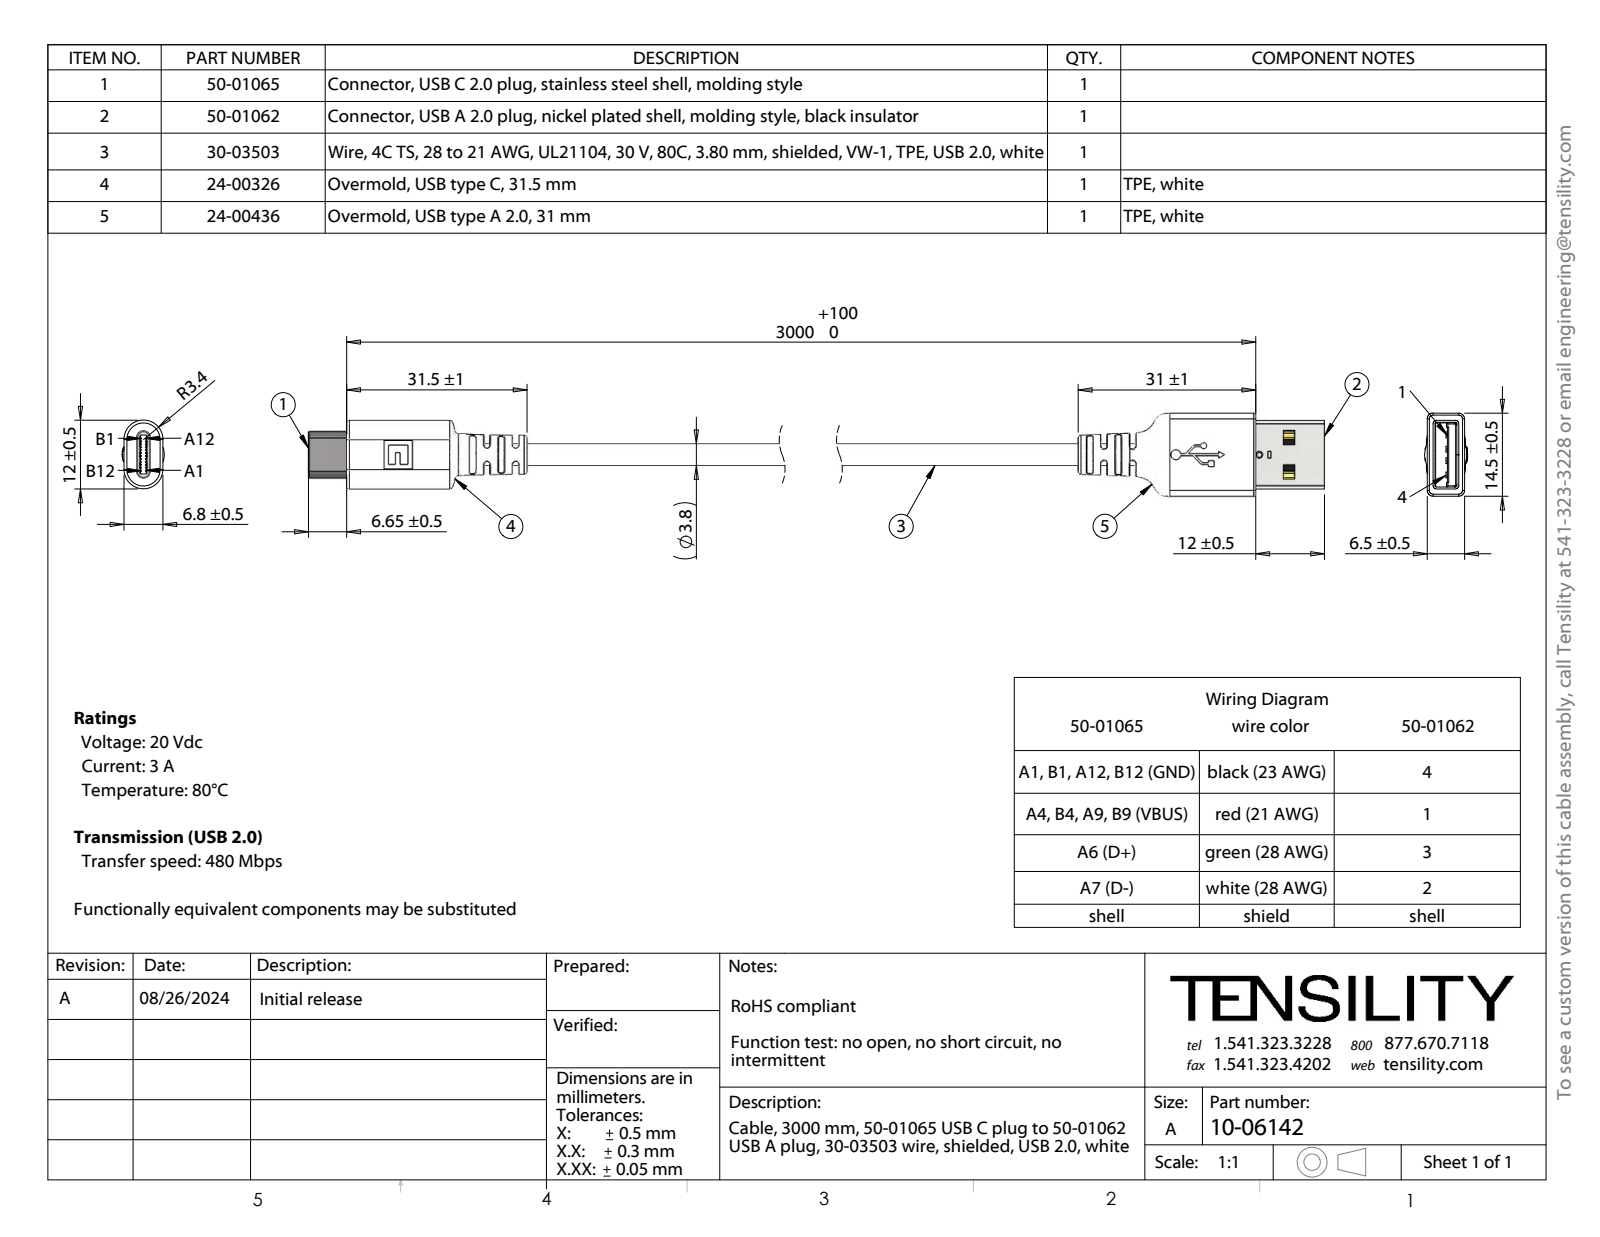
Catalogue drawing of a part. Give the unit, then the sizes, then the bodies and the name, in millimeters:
Units: millimetres
Overall size (bounding box): 211.15 × 14.5 × 7.54
Round holes (diameter × count): ⌀1.04 ×1, ⌀1.74 ×1, ⌀2.61 ×1, ⌀2.64 ×1, ⌀2.84 ×1
Round bosses / shafts (diameter × count): ⌀0.83 ×2, ⌀3.8 ×1, ⌀2.63 ×1, ⌀1.2 ×1, ⌀1 ×1
Partial cylindrical surfaces — rounded edges, fillets, slot ends (radius × count): R0.25 ×40, R0.2 ×34, R0.5 ×32, R0.35 ×14, R0.4 ×14, R0.3 ×13, R0.31 ×5, R0.6 ×5
Main face-to-face distances: 0.35, 4.15, 1, 5.5, 1.35, 5.15, 1.5, 2.5, 4.5, 3.8
Hole centre spacings: 5.11
Volume: 5 918 mm³ · Surface area: 22 580 mm²
Bodies: 125 solids, 1970 faces (1014 planar, 630 cylindrical, 326 other)
Part name (STEP PRODUCT): 50-01062_shell2; 50-01062_insulator_model; 24-00326; 50-01062_crimp_Assembled (+8 more)
STEP written by: SolidWorks 2021 (CONFIG_CONTROL_DESIGN)
